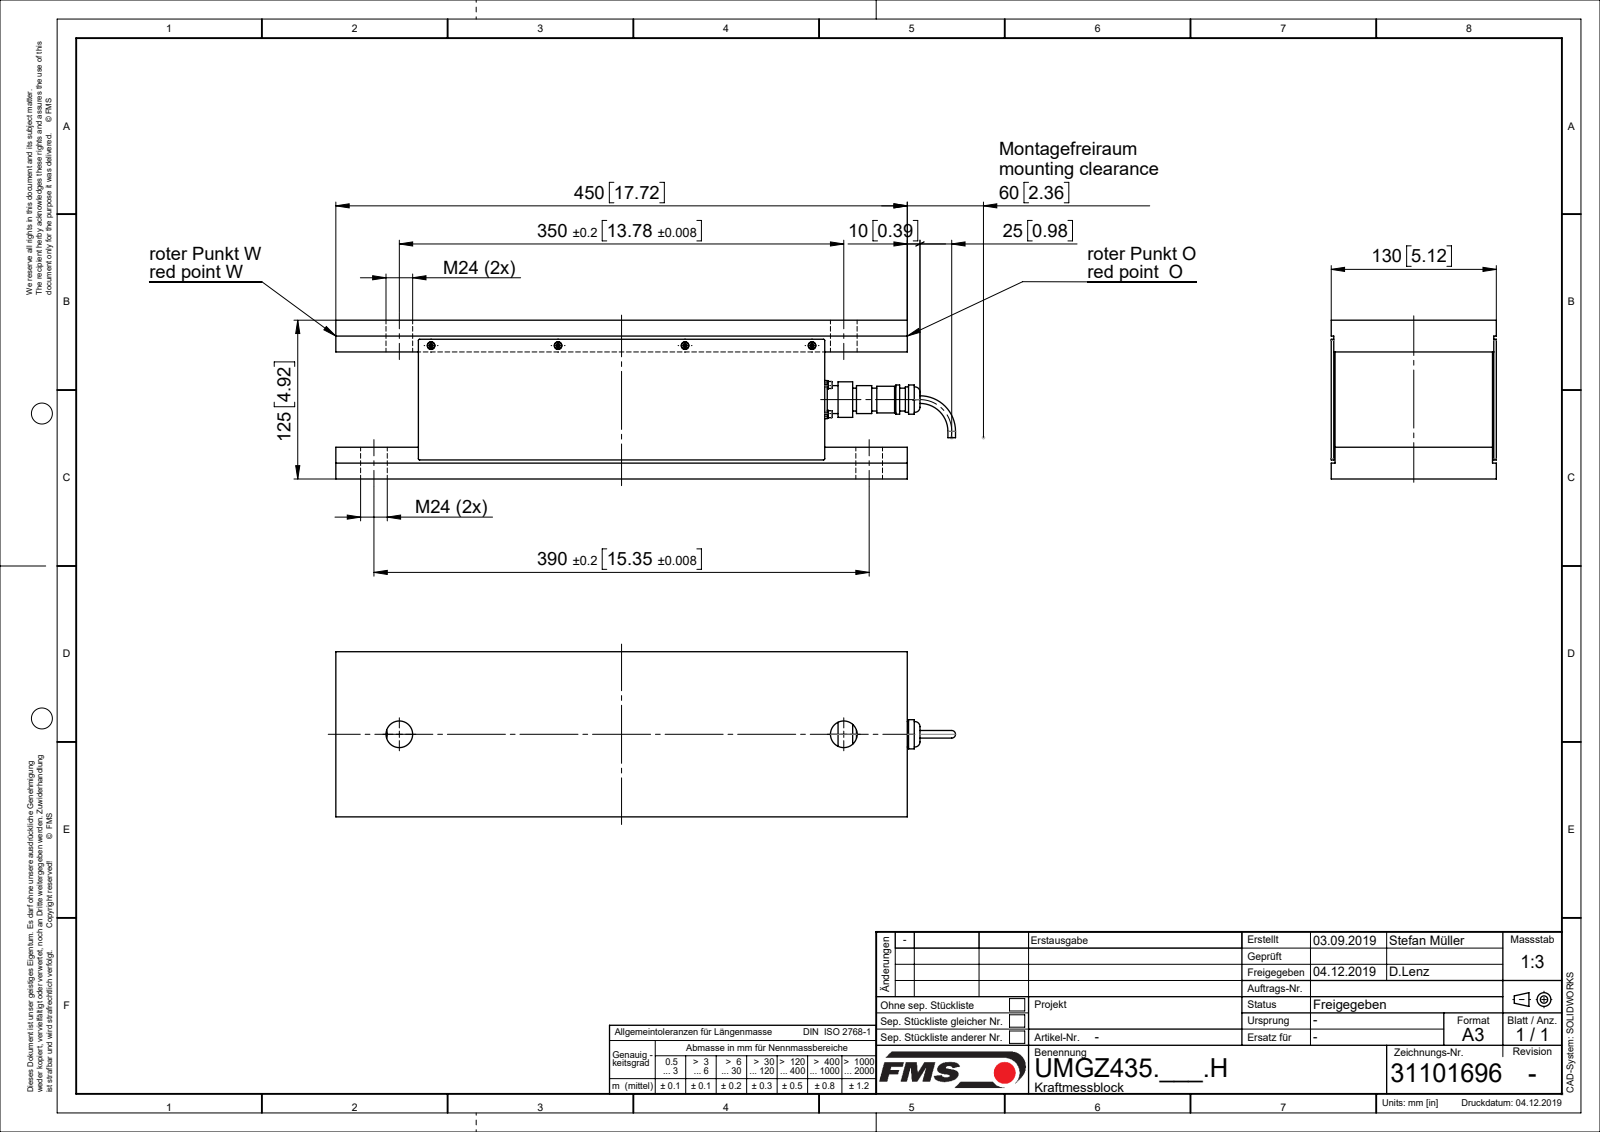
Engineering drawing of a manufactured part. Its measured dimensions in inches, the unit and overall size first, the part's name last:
Units: inches
Overall size (bounding box): 19.213 × 5.118 × 4.921
Round holes (diameter × count): ⌀0.098 ×8, ⌀0.122 ×4, ⌀0.126 ×4, ⌀0.142 ×4, ⌀0.236 ×4, ⌀0.827 ×4
Round bosses / shafts (diameter × count): ⌀0.118 ×8, ⌀0.244 ×4, ⌀0.224 ×4, ⌀0.217 ×4, ⌀0.098 ×4, ⌀1.102 ×1, ⌀0.906 ×1, ⌀0.866 ×1
Partial cylindrical surfaces — rounded edges, fillets, slot ends (radius × count): R0.039 ×4, R0.157 ×4, R0.492 ×4
Main face-to-face distances: 0.984, 4.921, 0.079, 5.039, 3.937, 5.118, 4.961, 4.134, 0.906, 4.055
Hole centre spacings: 0.906, 3.937, 0.787, 1.281, 7.874, 14.567, 11.811, 13.78
Volume: 291.8 in³ · Surface area: 804.1 in²
Bodies: 20 solids, 495 faces (209 planar, 194 cylindrical, 92 other)
Part name (STEP PRODUCT): Federringe_DIN127A_M03; 51130.03_01; 51132_01; 31101648_01 (+3 more)
STEP written by: SolidWorks 2018 (CONFIG_CONTROL_DESIGN)
